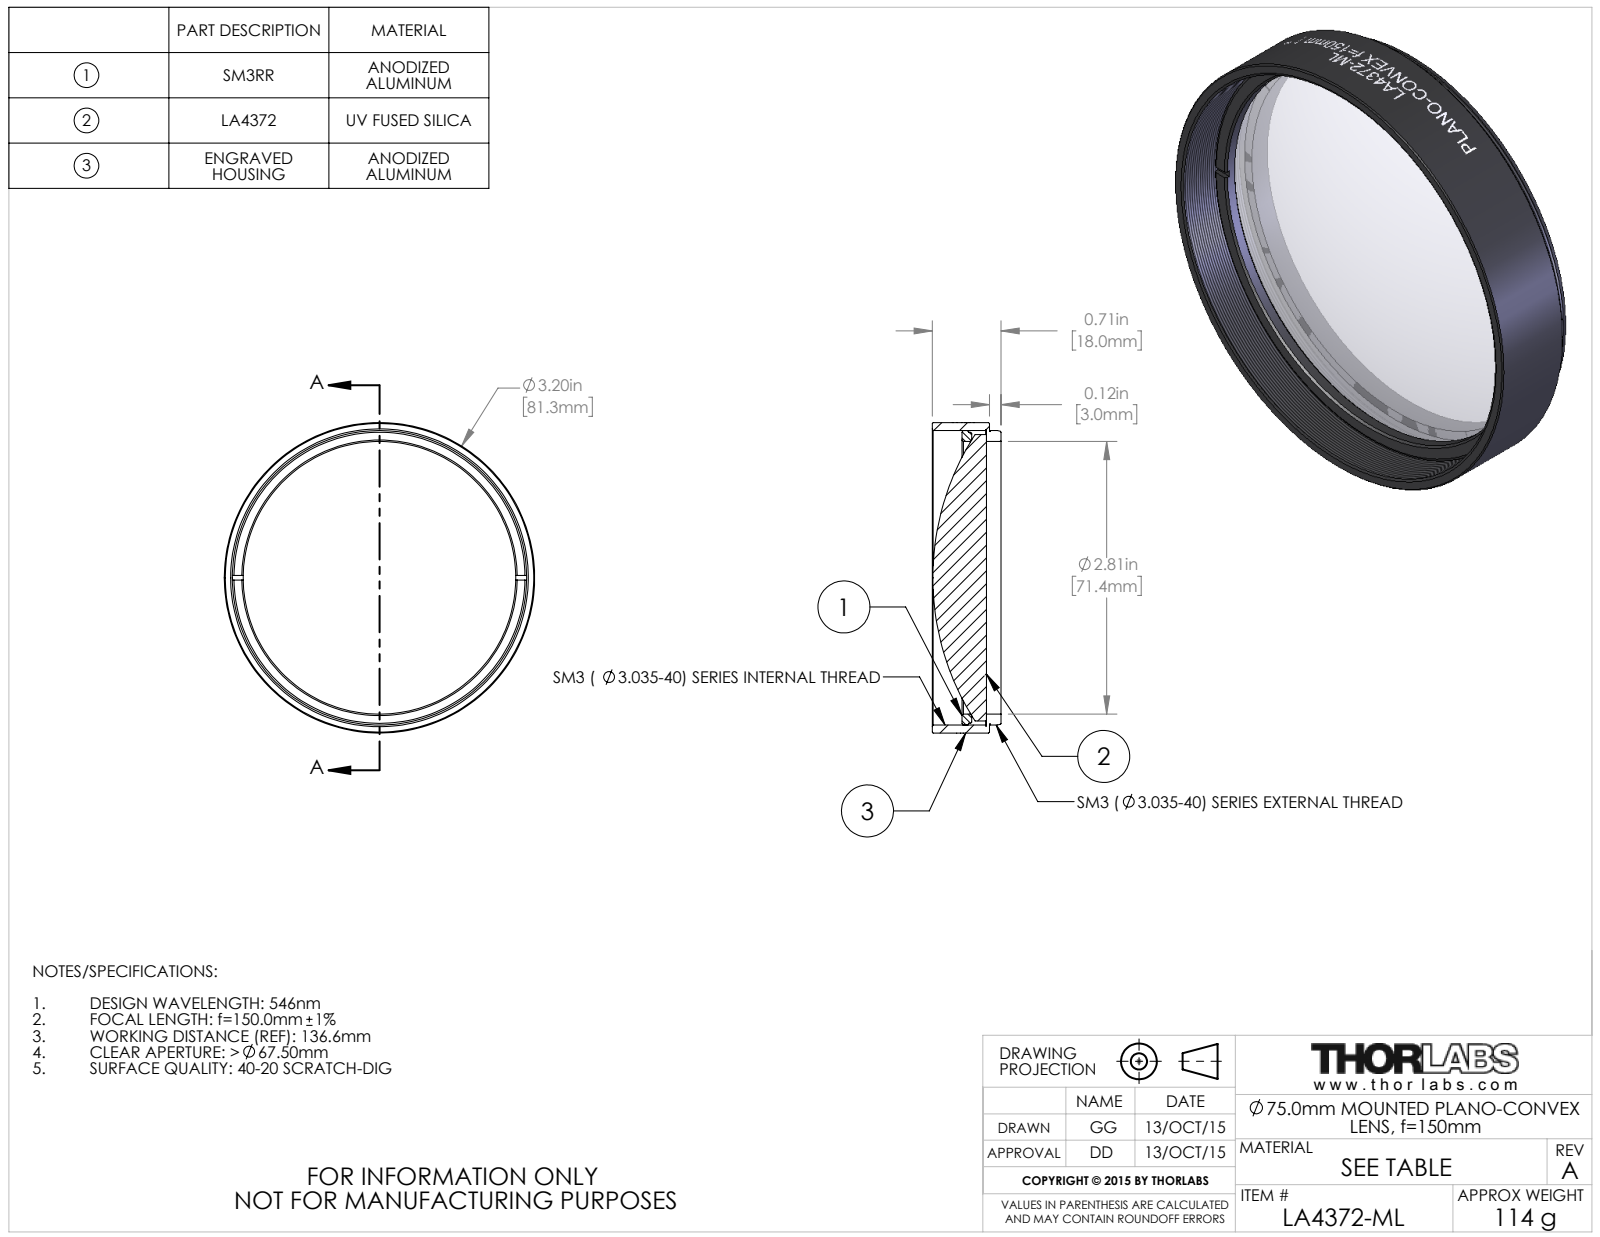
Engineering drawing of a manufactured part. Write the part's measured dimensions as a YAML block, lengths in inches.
part_name: "TTN039255-E0W"
step_written_by: "SolidWorks 2016 (CONFIG_CONTROL_DESIGN)"
units: inches
bodies: {solids: 3, faces: 114, planar: 17, cylindrical: 73, other: 24}
overall_size: [3.2, 3.2, 0.71]
volume: 3.061
surface_area: 36.45
round_holes:
  - {diameter: 2.81, count: 1}
  - {diameter: 3.055, count: 1}
round_bosses_or_shafts:
  - {diameter: 3.2, count: 1}
  - {diameter: 3.035, count: 1}
  - {diameter: 3.015, count: 1}
  - {diameter: 2.998, count: 1}
  - {diameter: 2.953, count: 1}
face_to_face_distances: [0.15, 0.12, 0.03, 0.404, 0.283, 0.254, 0.304, 0.183, 0.154, 0.1]
